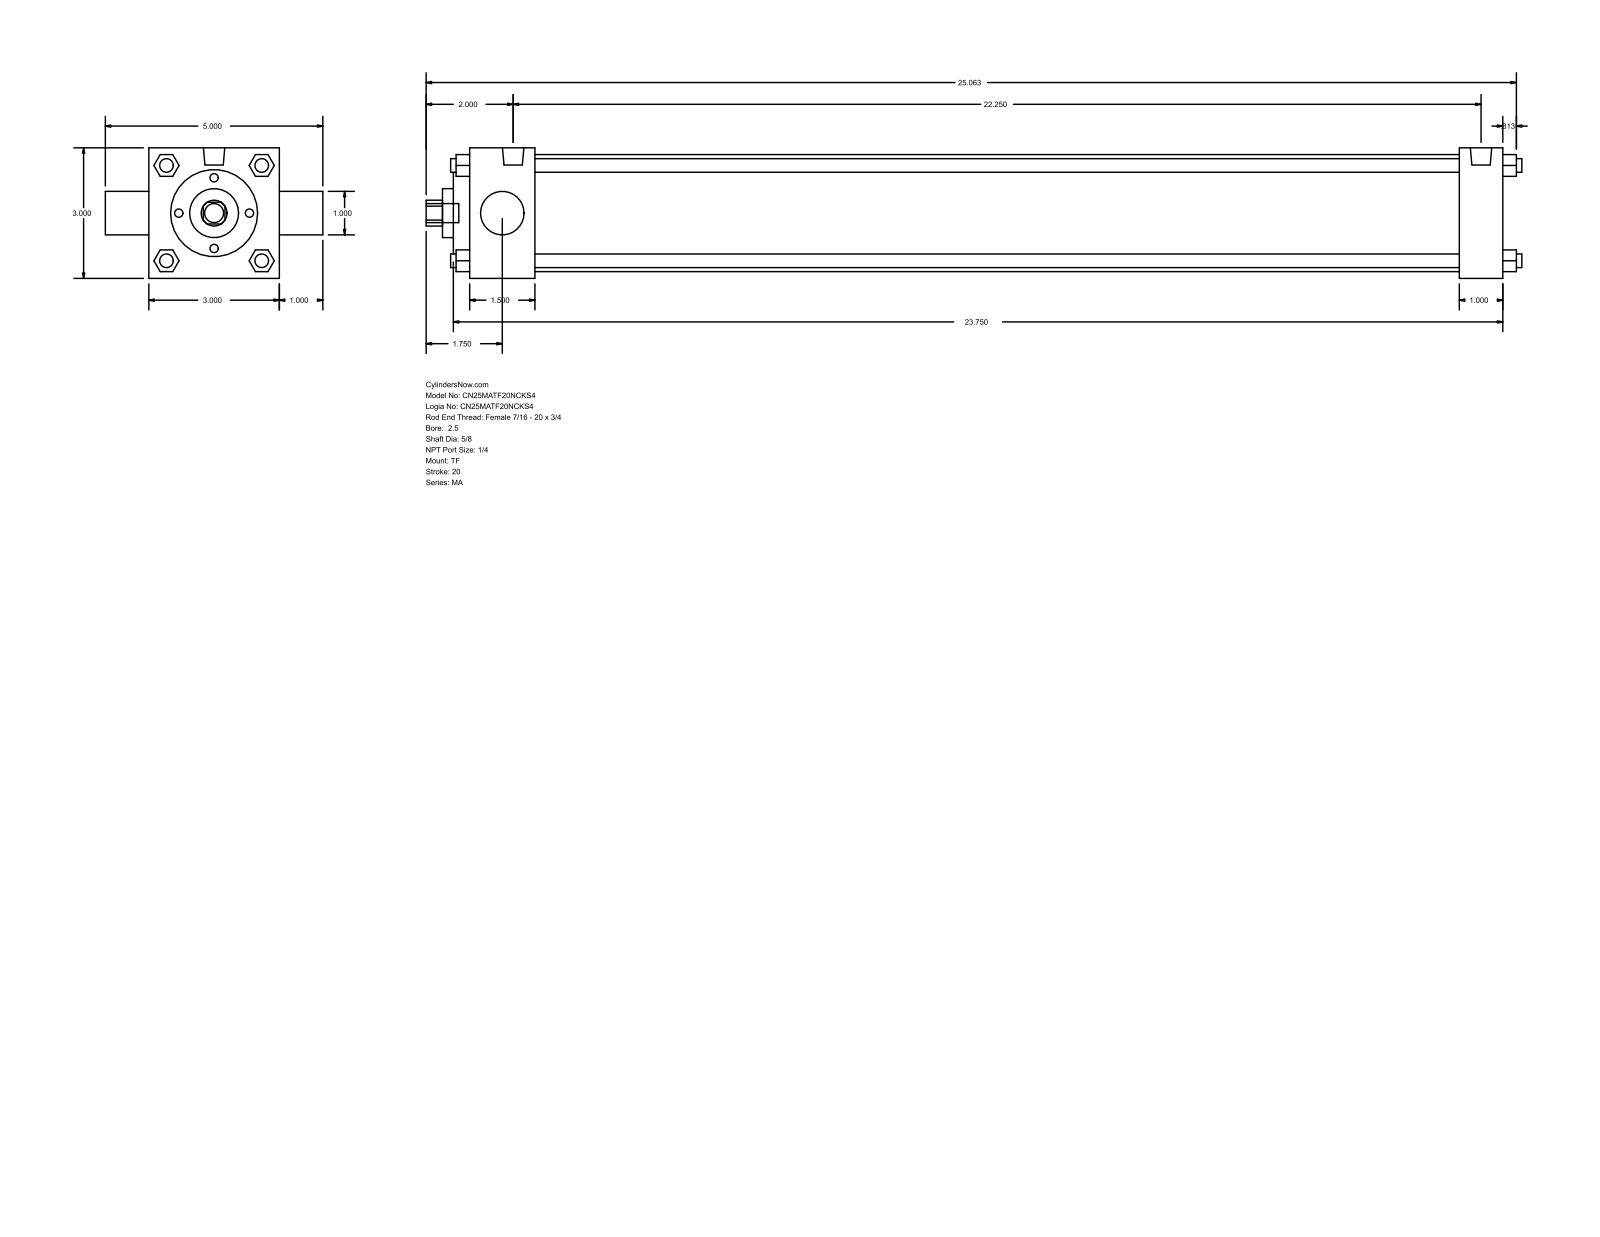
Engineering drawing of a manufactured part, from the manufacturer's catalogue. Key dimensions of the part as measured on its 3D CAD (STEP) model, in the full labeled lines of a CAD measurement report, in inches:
Part name (STEP PRODUCT): MA_TF__0250_0.625
STEP written by: GSSL Pune (CONFIG_CONTROL_DESIGN)
Units: inches
Bodies: 0 solids, 122 faces (93 planar, 29 cylindrical, 0 other)
Overall size (bounding box): 25.187 × 5 × 3
Round holes (diameter × count): ⌀0.625 ×1, ⌀1 ×1, ⌀1.125 ×1, ⌀2 ×1, ⌀2.69 ×1
Round bosses / shafts (diameter × count): ⌀0.313 ×7, ⌀0.492 ×2, ⌀0.437 ×1
Partial cylindrical surfaces — rounded edges, fillets, slot ends (radius × count): R0.297 ×1
Main face-to-face distances: 3, 23.75, 1, 1.5, 22.75, 21.25, 22.25, 0.5, 0.375, 1.875
